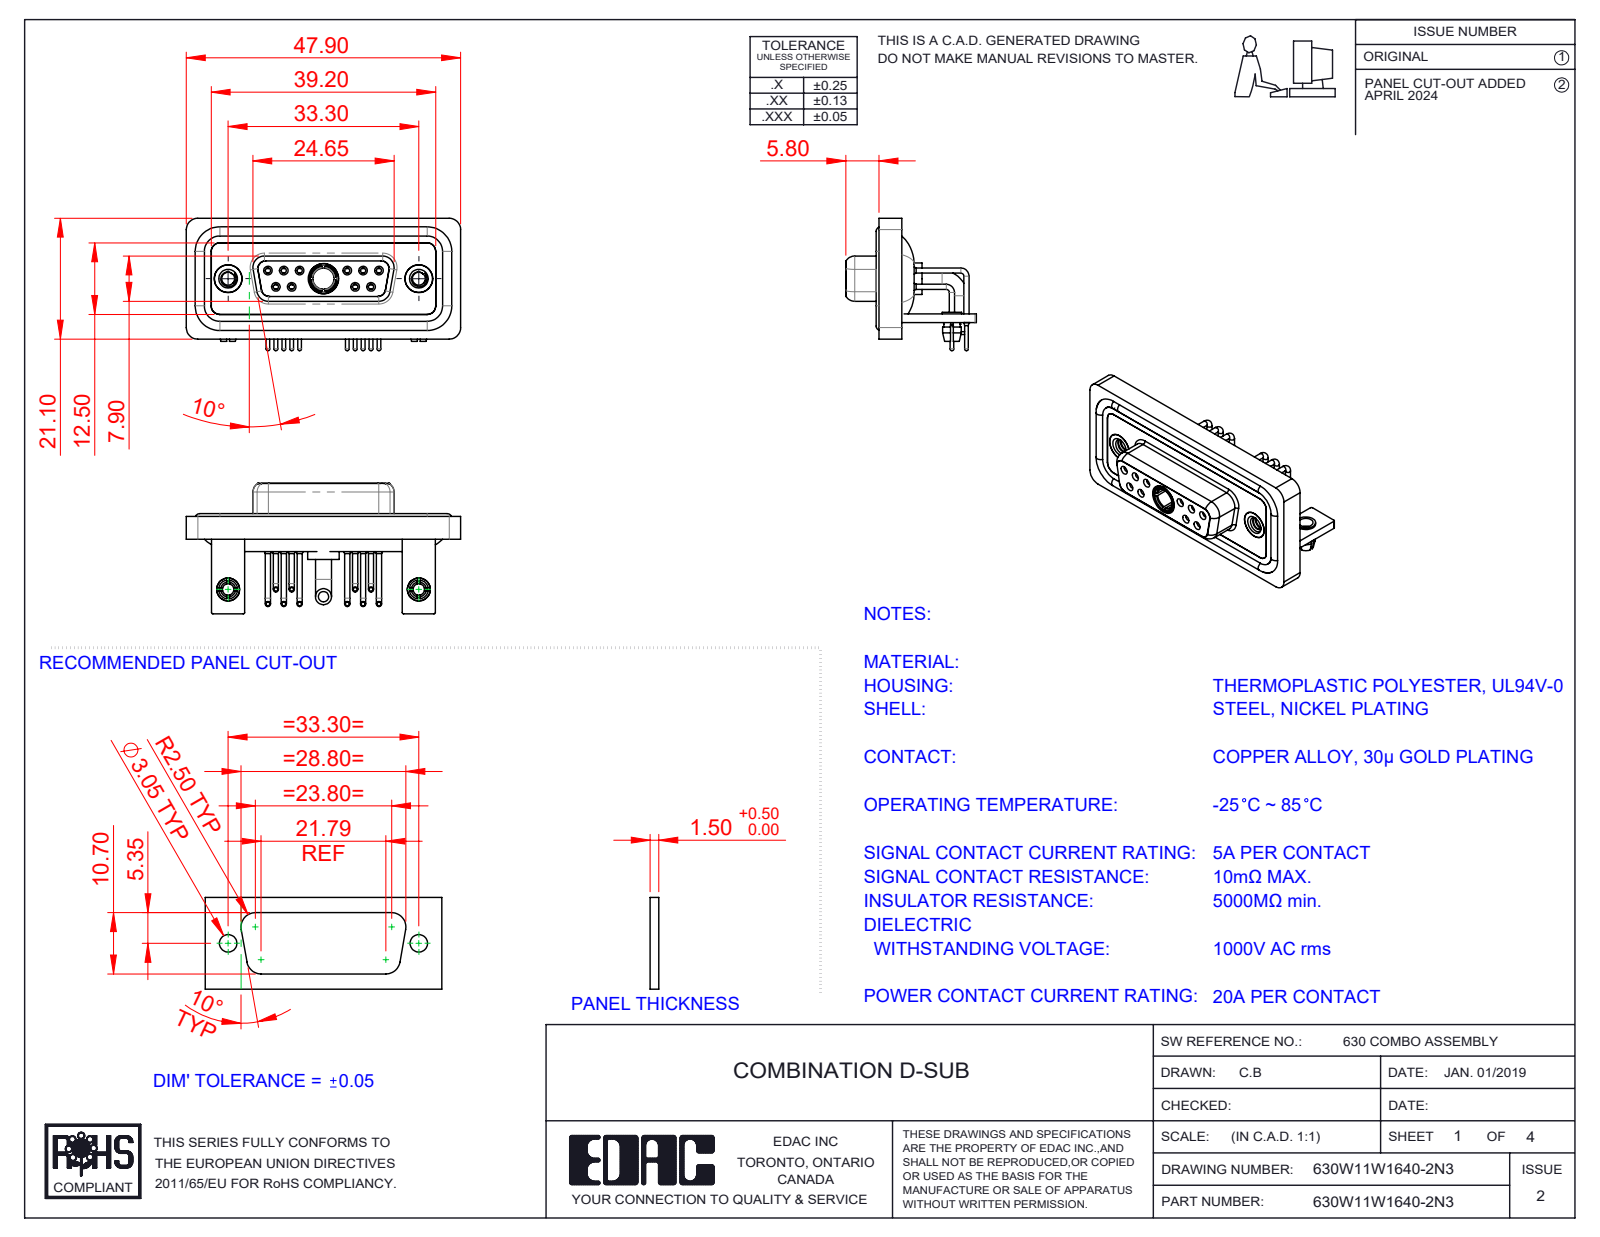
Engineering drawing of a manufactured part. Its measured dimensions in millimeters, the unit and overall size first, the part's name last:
Units: millimetres
Overall size (bounding box): 47.9 × 23.12 × 22.8
Round holes (diameter × count): ⌀2 ×12, ⌀0.9 ×10, ⌀1.1 ×10, ⌀1.5 ×10, ⌀1.7 ×6, ⌀1.6 ×4, ⌀4.85 ×3, ⌀2.26 ×2, ⌀2.5 ×2, ⌀3.2 ×2, ⌀4 ×2, ⌀4.05 ×2
Round bosses / shafts (diameter × count): ⌀1.6 ×10, ⌀0.9 ×10, ⌀0.65 ×10, ⌀4.95 ×2, ⌀4.8 ×2, ⌀4 ×2, ⌀3.4 ×2, ⌀3.3 ×2
Partial cylindrical surfaces — rounded edges, fillets, slot ends (radius × count): R2 ×21, R1.5 ×18, R0.25 ×16, R1.35 ×12, R1.6 ×8, R0.5 ×5, R0.6 ×4, R0.65 ×4
Main face-to-face distances: 0.4, 2.9, 1.5, 1.8, 3.7, 1.1, 1.6, 4.1, 0.8, 2.5
Hole centre spacings: 3.16, 2.77, 13.85, 11.08, 16.62, 5.03, 5.04, 5.54
Volume: 6 620 mm³ · Surface area: 11 417 mm²
Bodies: 23 solids, 1134 faces (352 planar, 499 cylindrical, 283 other)
Part name (STEP PRODUCT): 630Combo Housing_11W1; 630Combo Waterproof Housing_15 Contacts; 630W11W1640-2N3; Power Socket_20A RA (+7 more)
STEP written by: SolidWorks 2023 (CONFIG_CONTROL_DESIGN)
